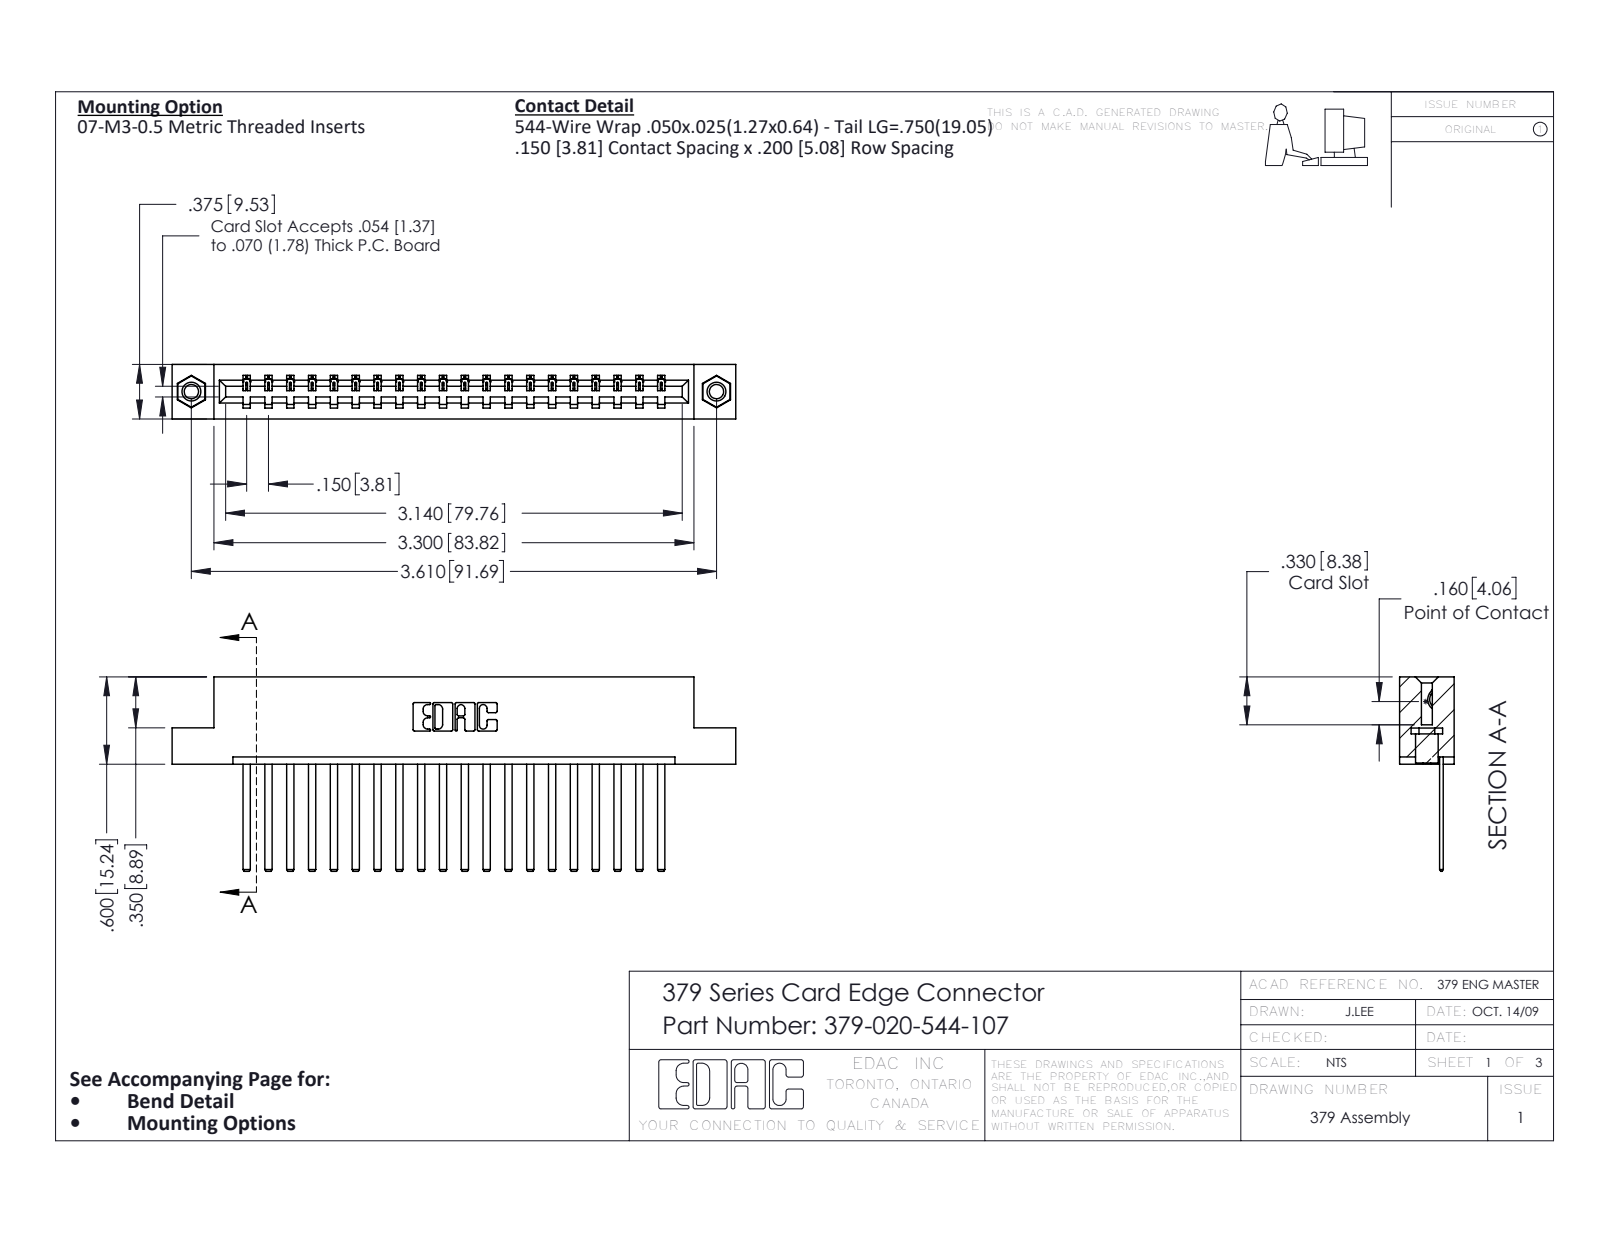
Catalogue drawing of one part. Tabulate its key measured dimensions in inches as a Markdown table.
| quantity | value |
| --- | --- |
| part name | 379 Part_Flush - .156 Dia - TI; 379-020-544-107; 345-292-001_345-293-144; 345-250-001_345-250-005-103 |
| STEP written by | SolidWorks 2016 (CONFIG_CONTROL_DESIGN) |
| units | inches |
| bodies | 23 solids, 1214 faces (862 planar, 336 cylindrical, 16 other) |
| overall size | 3.875 × 1.337 × 0.375 |
| volume | 0.628 in³ |
| surface area | 17.41 in² |
| round holes (diameter × count) | 0.098 × 2, 0.125 × 2, 0.156 × 2 |
| round bosses / shafts (diameter × count) | 0.155 × 2 |
| partial cylindrical surfaces (radius × count) | 0.006 × 40, 0.01 × 22, 0.007 × 6, 0.031 × 6, 0.026 × 3, 0.014 × 1, 0.022 × 1, 0.024 × 1 |
| main face-to-face distances | 0.3, 0.075, 0.375, 0.6, 0.275, 0.1, 0.025, 0.15, 0.225, 0.45 |
| hole center spacings | 3.61 |
